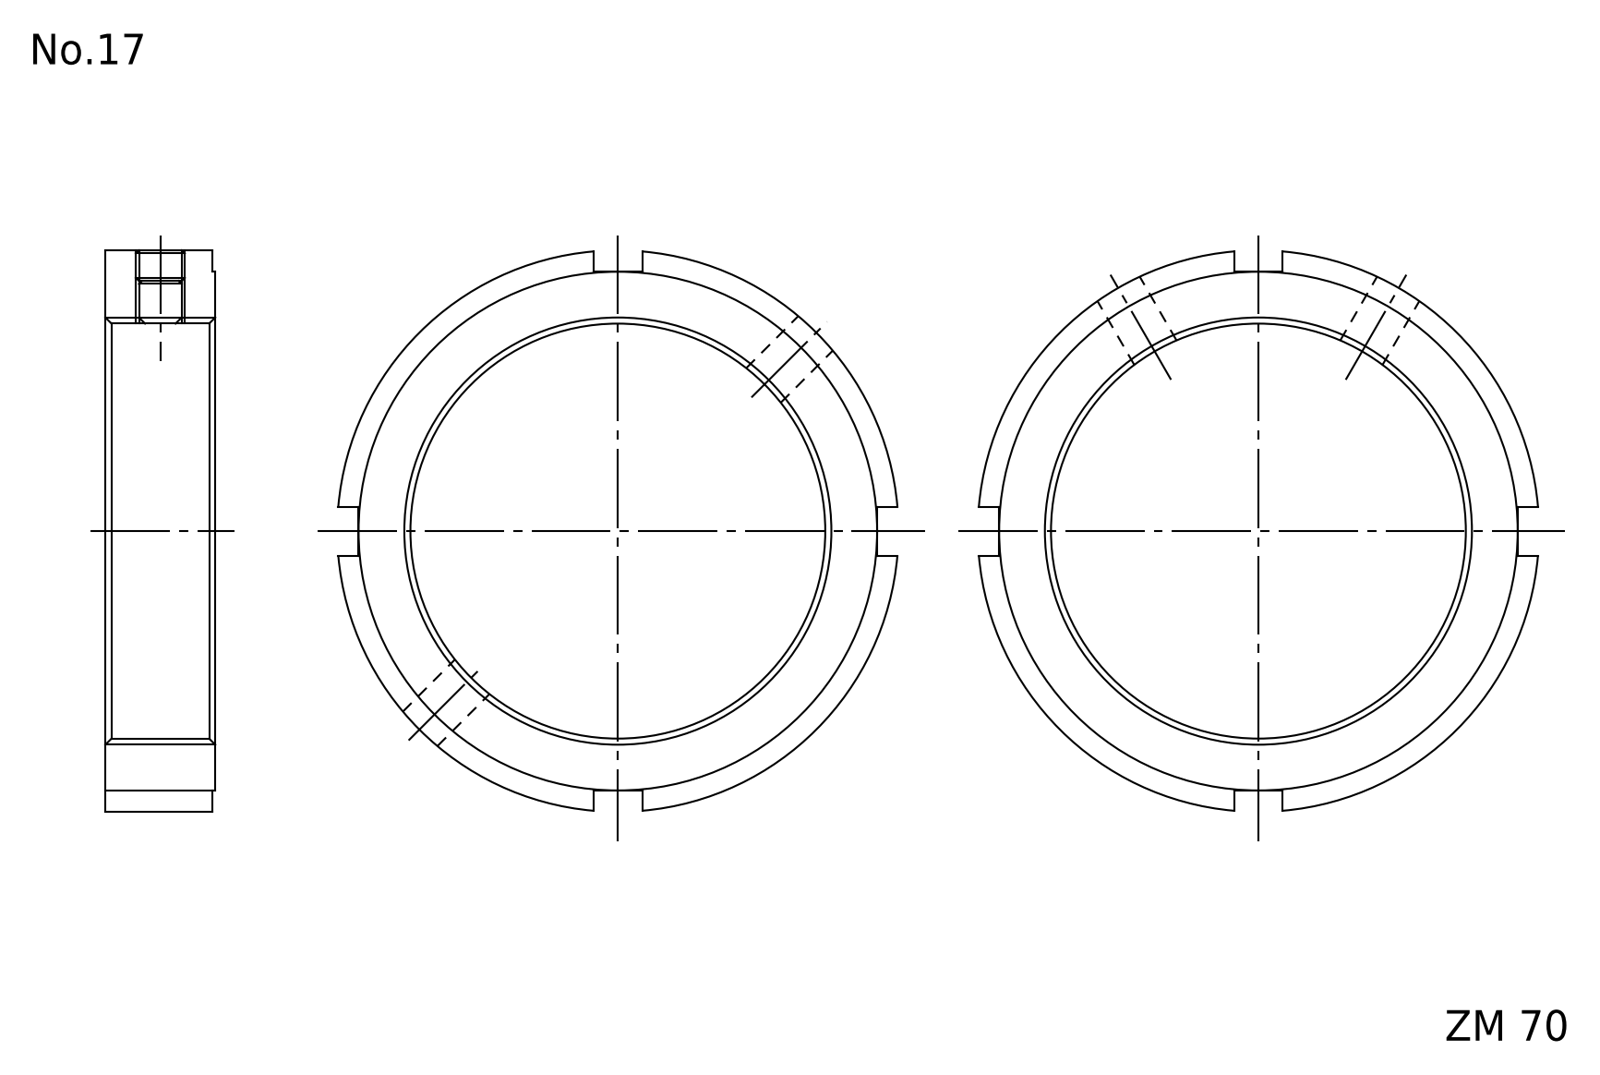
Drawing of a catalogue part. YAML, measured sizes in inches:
part_name: "FKD ZM 70"
step_written_by: "Autodesk Inventor 2011 (AUTOMOTIVE_DESIGN)"
units: inches
bodies: {solids: 1, faces: 26, planar: 18, cylindrical: 8, other: 0}
overall_size: [3.608, 3.608, 0.709]
volume: 2.881
surface_area: 23.74
round_holes:
  - {diameter: 0.262, count: 2}
  - {diameter: 2.756, count: 1}
round_bosses_or_shafts:
  - {diameter: 3.622, count: 1}
  - {diameter: 3.346, count: 1}
face_to_face_distances: [0.709, 0.02, 0.689, 1.516, 1.831, 3.346, 0.315]
